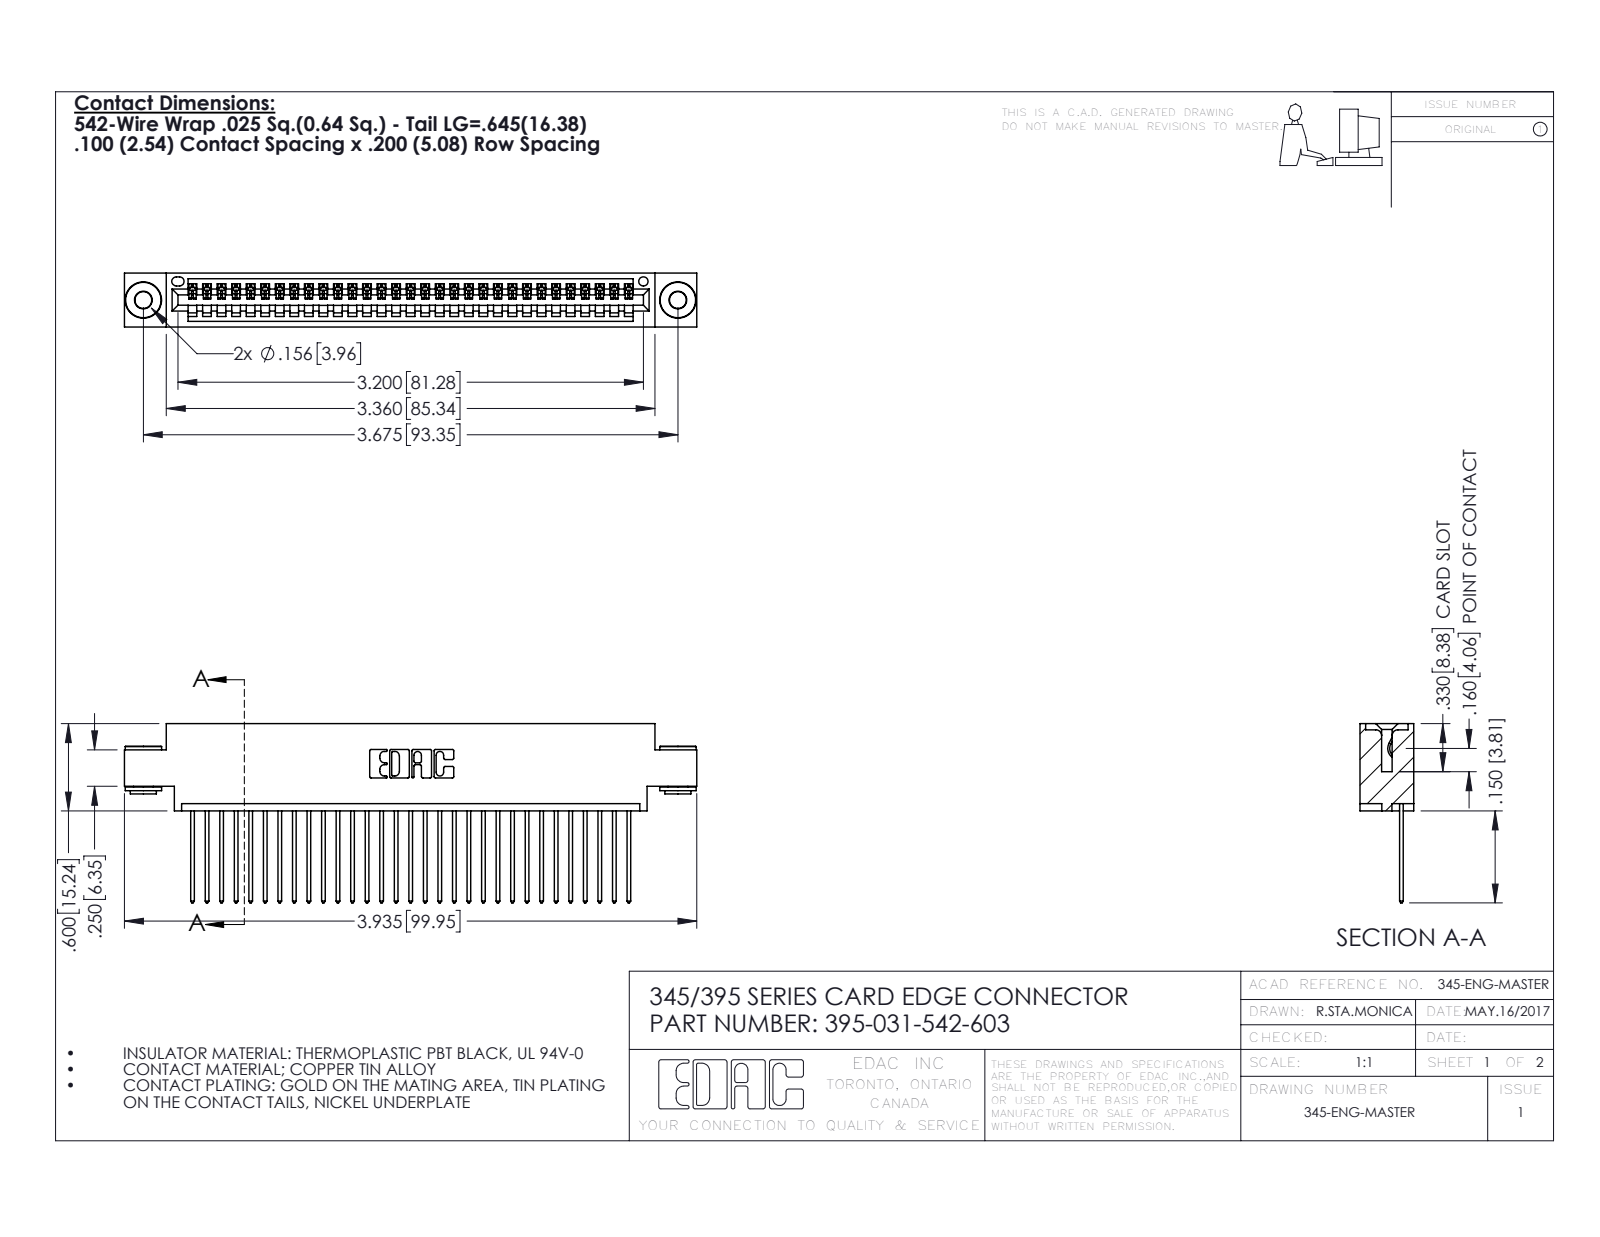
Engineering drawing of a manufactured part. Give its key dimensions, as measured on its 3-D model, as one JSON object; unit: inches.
{"part_name": "345-292-001_345-293-142; 395-031-542-603; 345 Part_0.170 Offset - 0.156 Dia-TH; 345-250-002_345-250-002-102", "step_written_by": "SolidWorks 2016 (CONFIG_CONTROL_DESIGN)", "units": "inches", "bodies": {"solids": 34, "faces": 1966, "planar": 1334, "cylindrical": 624, "other": 8}, "overall_size": [3.935, 1.232, 0.37], "volume_in3": 0.572, "surface_area_in2": 20.29, "round_holes": [[0.116, 2], [0.156, 2], [0.064, 1]], "round_bosses_or_shafts": [[0.25, 2], [0.18, 2], [0.136, 2]], "partial_cylinders_radius": [[0.006, 62], [0.01, 62], [0.01, 22], [0.007, 6], [0.031, 6], [0.026, 3], [0.031, 2], [0.04, 2]], "face_to_face_distances": [0.072, 0.298, 0.37, 0.098, 0.272, 0.025, 0.2, 0.225, 0.175, 0.149], "hole_center_spacings": [0.27, 3.44, 3.675]}
